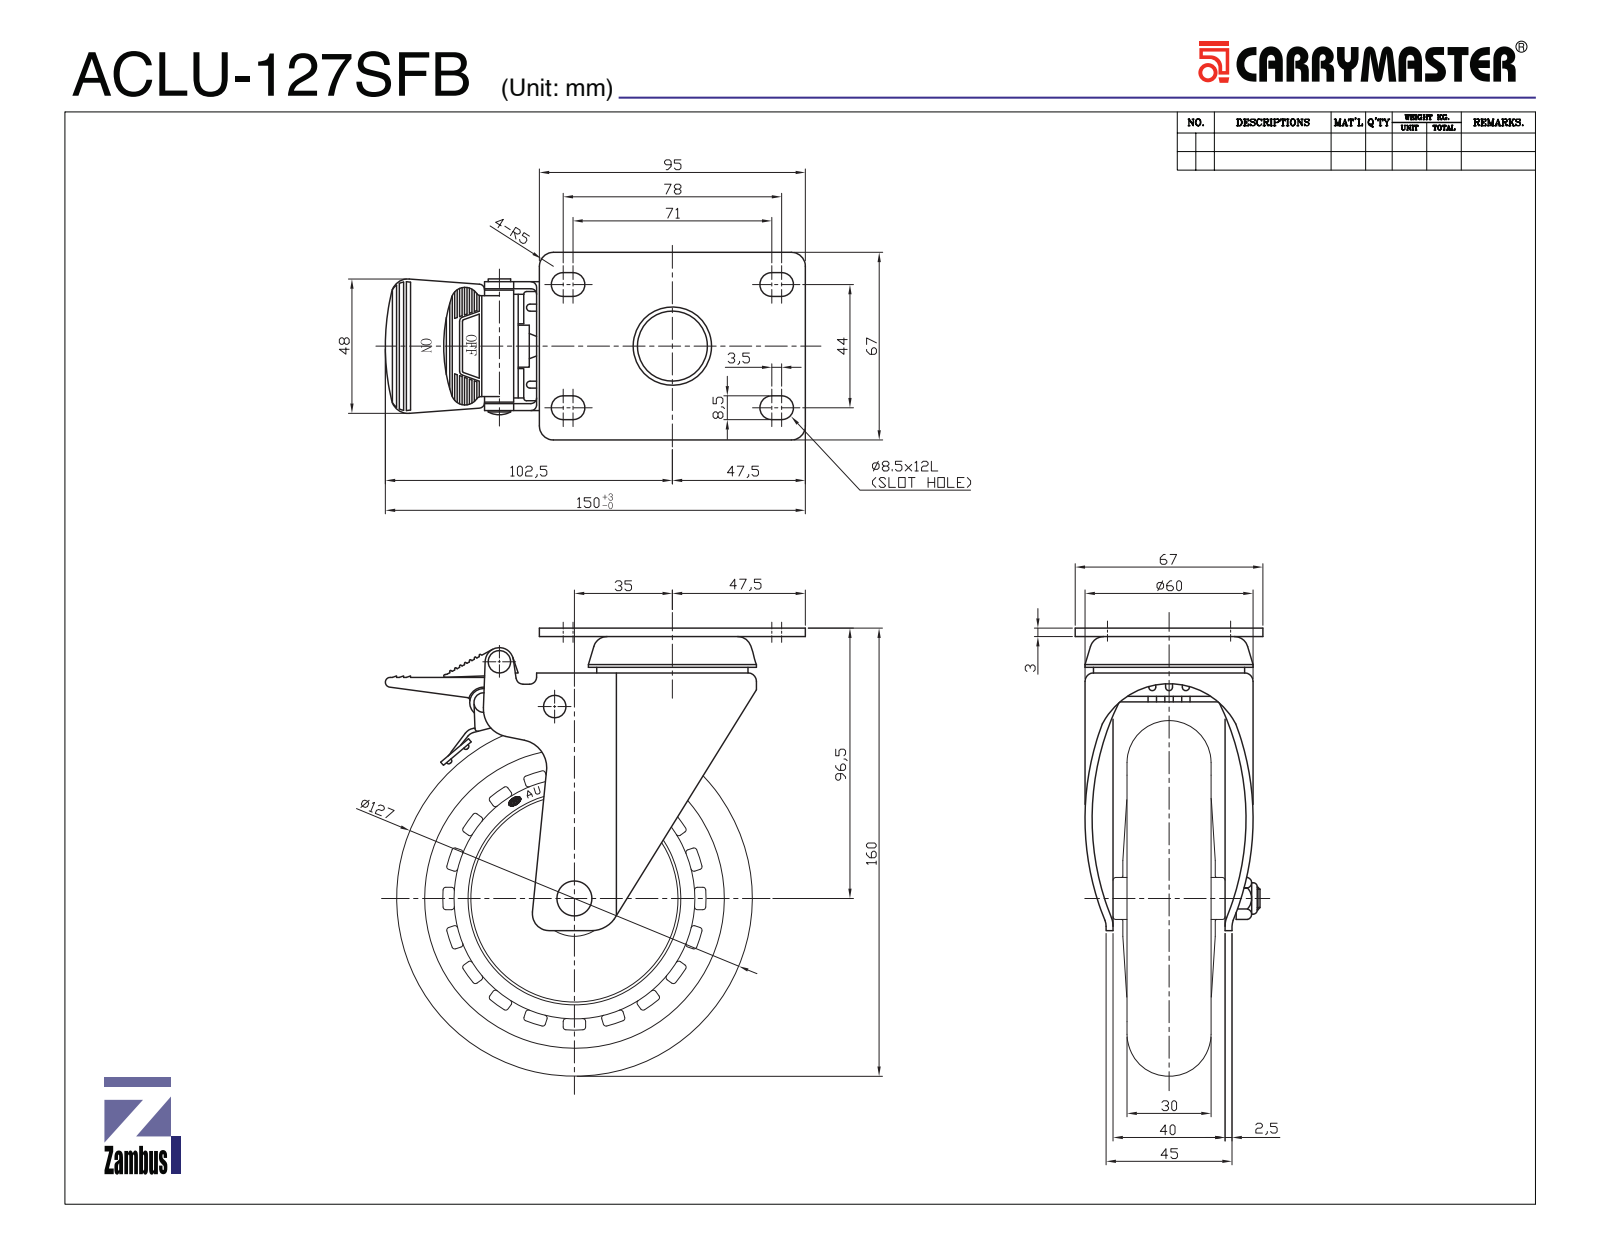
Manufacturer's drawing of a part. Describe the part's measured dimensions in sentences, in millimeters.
The part is named "ACLU-100SF TOP PLATE; ACLU-127 WHEEL COVER; ACLU-127 WHEEL CORE; ACLU-127 WHEEL URETHANE (+7 more)". Its 3-D file was written by "SolidWorks 2018 (CONFIG_CONTROL_DESIGN)". It is 22 solids with 1665 faces: 852 planar, 495 cylindrical and 318 other. Overall it measures 161 by 153.47 by 69.56 millimeters. Its volume is 444 512 cubic millimeters and its surface area 196 002 square millimeters. Round holes: 2 of diameter 3.5, 2 of diameter 4.3, 2 of diameter 5.2, 1 of diameter 5.3, 1 of diameter 6.8, 1 of diameter 8, 1 of diameter 9.6, 1 of diameter 12.6, 1 of diameter 14, 1 of diameter 19.6, 1 of diameter 22, 1 of diameter 28.62. Round bosses or shafts: 2 of diameter 9, 2 of diameter 4.9, 1 of diameter 108, 1 of diameter 73, 1 of diameter 59.7, 1 of diameter 54, 1 of diameter 38, 1 of diameter 31. Partial cylindrical surfaces (rounded edges, fillets, slot ends): 83 of radius 1, 20 of radius 0.2, 19 of radius 3.86, 16 of radius 25, 8 of radius 4.25, 8 of radius 5, 6 of radius 2, 6 of radius 6. The main face-to-face distances are 3, 5, 30.5, 5.5, 13, 2.5, 7.5, 8, 0.5, 11.8. The hole center spacings are 9.7, 12.81, 17.54, 17.62, 25.74, 26.08, 70.54, 76.5.
